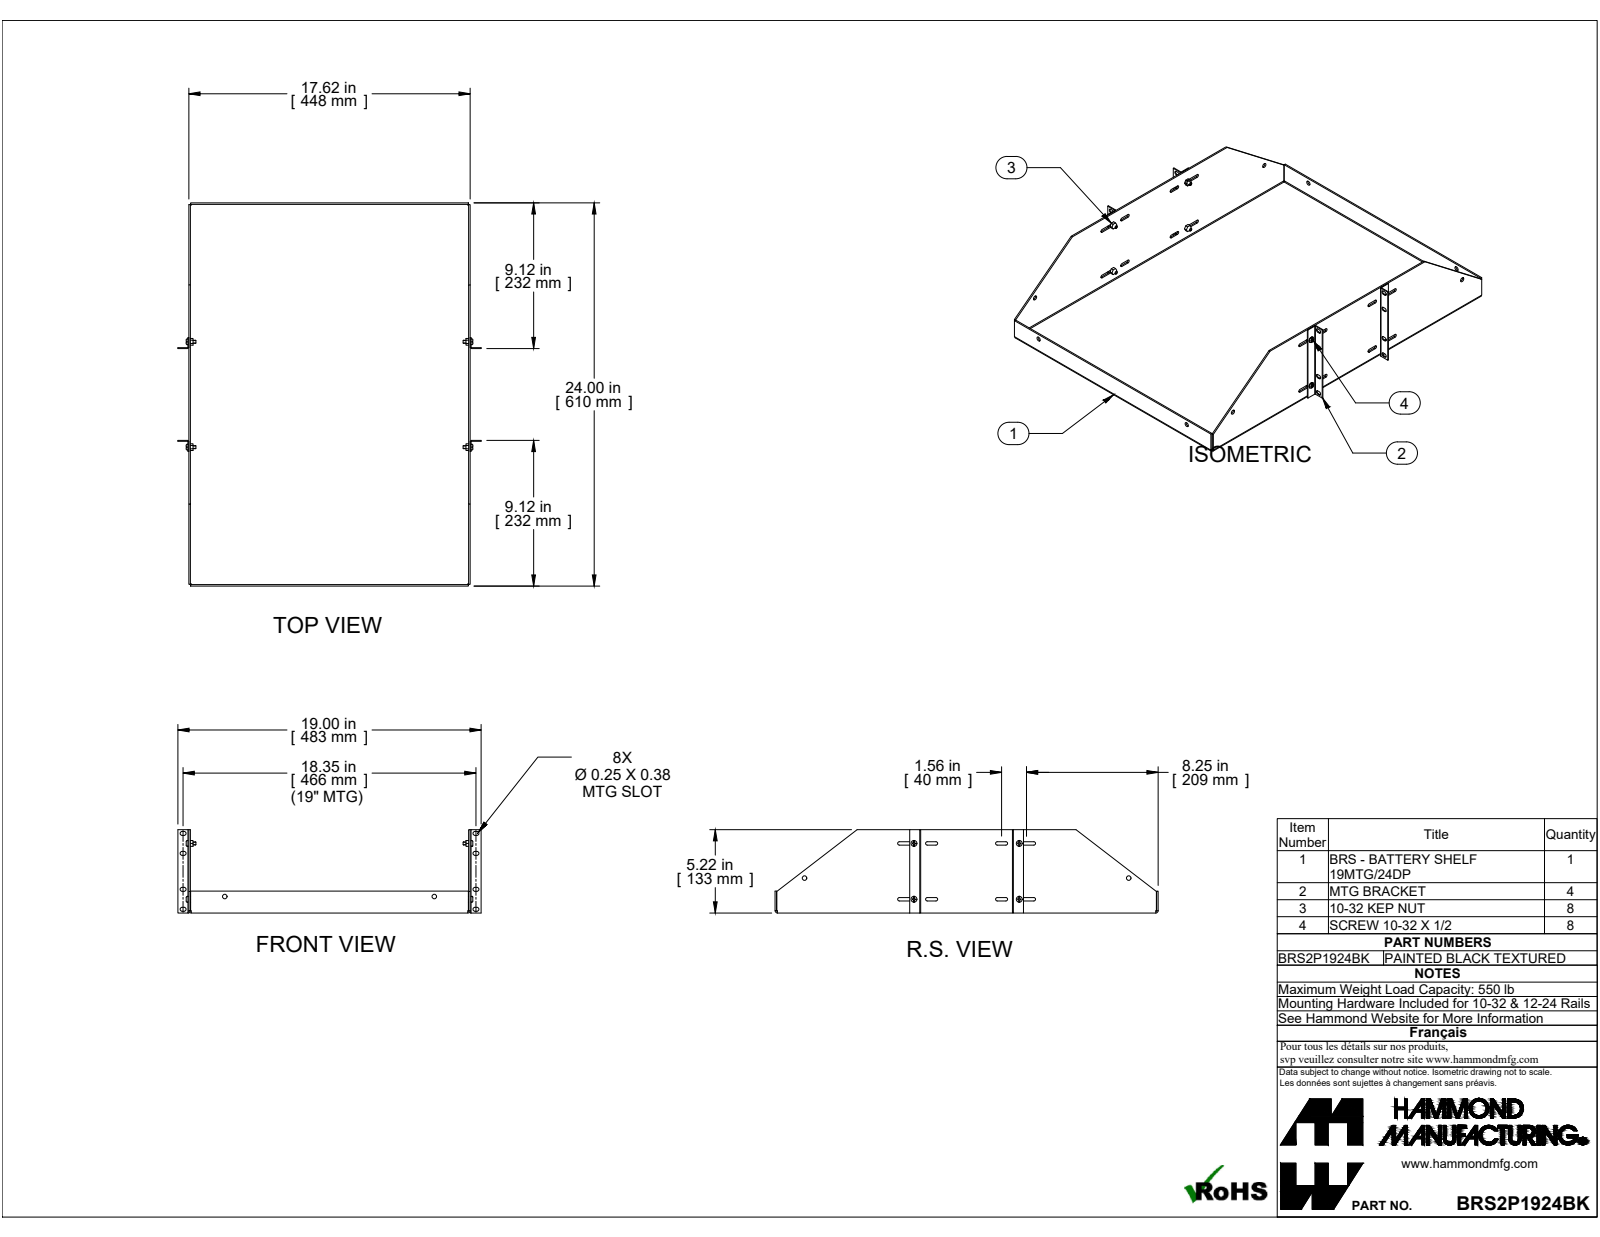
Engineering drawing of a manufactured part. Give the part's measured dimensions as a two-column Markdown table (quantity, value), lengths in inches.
| quantity | value |
| --- | --- |
| part name | BRS2P1924BK |
| STEP written by | SolidWorks 2019 (CONFIG_CONTROL_DESIGN) |
| units | inches |
| bodies | 21 solids, 466 faces (322 planar, 120 cylindrical, 24 other) |
| overall size | 24 × 19 × 5.218 |
| volume | 64.96 in³ |
| surface area | 1 408 in² |
| round holes (diameter × count) | 0.156 × 4, 0.213 × 4, 0.281 × 4 |
| round bosses / shafts (diameter × count) | 0.37 × 4, 0.19 × 4 |
| partial cylindrical surfaces (radius × count) | 0.125 × 16, 0.106 × 12, 0.029 × 4, 0.048 × 4, 0.086 × 4, 0.143 × 4 |
| main face-to-face distances | 0.095, 17.53, 0.095, 17.625, 17.435, 23.905, 0.057, 24, 23.81, 0.152 |
| hole center spacings | 3.5, 6.597, 6.985, 7.194, 7.468, 13.52, 13.629, 13.125 |
